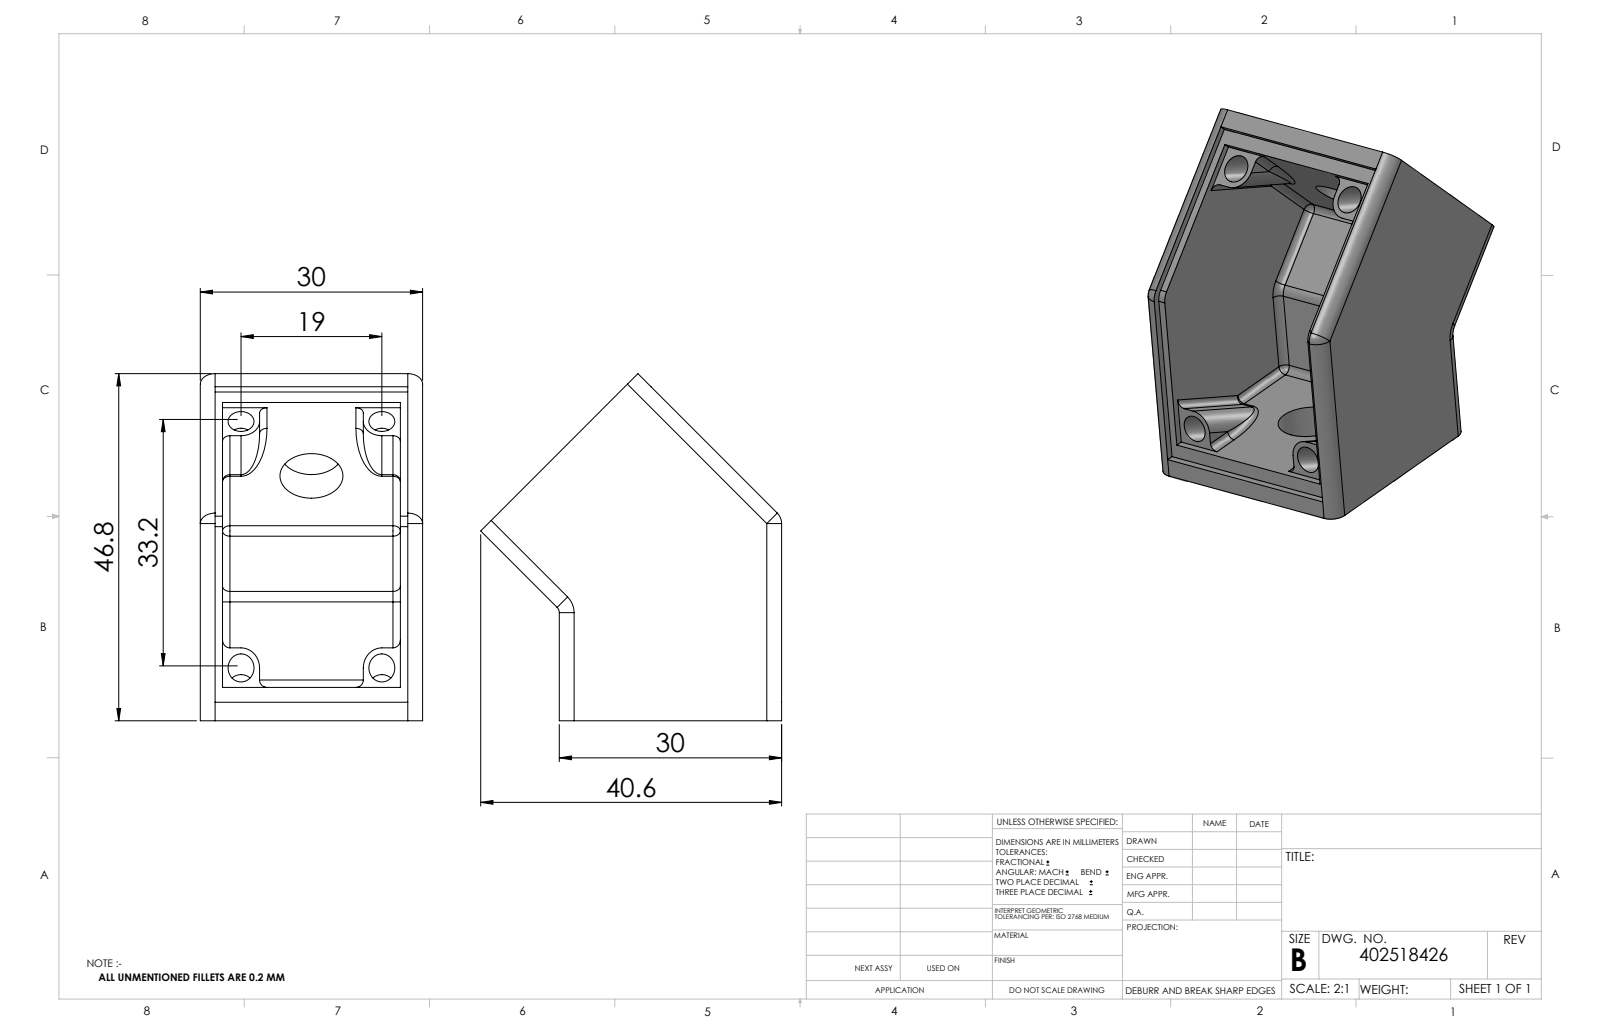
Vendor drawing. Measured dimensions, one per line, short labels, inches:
name: 402518426_c_1
written by: SolidWorks 2014 (CONFIG_CONTROL_DESIGN)
unit: in
bodies: 1 solid, 525 faces (124 planar, 254 cylindrical, 147 other)
size: 1.843 × 1.598 × 1.181
volume: 0.92 in³; area: 16.05 in²
holes: 4× ⌀0.138, 2× ⌀0.335
rounds: 136× R0.008, 21× R0.039, 16× R0.02, 10× R0.079, 4× R0.098
face distances: 0.118, 1.063, 1.181, 0.177, 0.945, 0.039, 0.083, 0.079, 0.146, 0.031
hole spacings: 0.748, 1.416, 1.601
